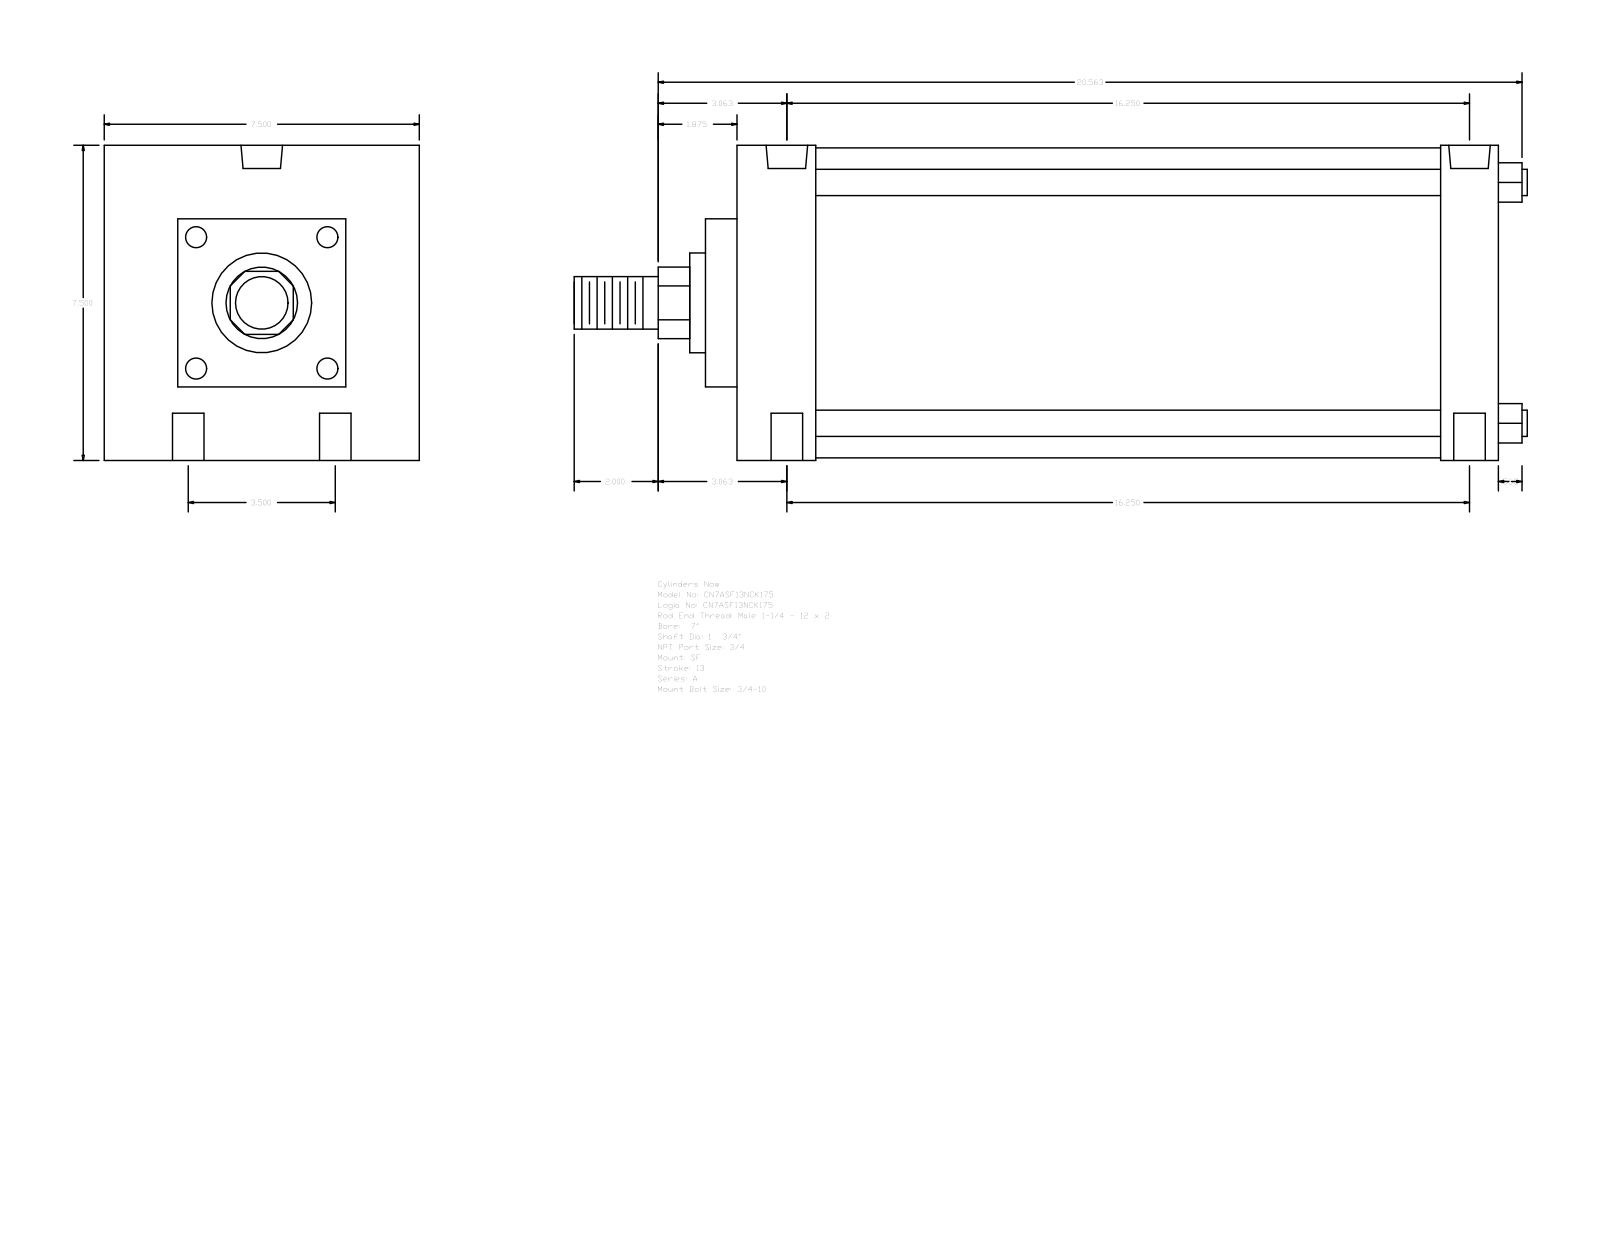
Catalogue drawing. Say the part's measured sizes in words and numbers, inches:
The part is named "A_SF__0700_1.75". Its 3-D file was written by "GSSL Pune (CONFIG_CONTROL_DESIGN)". It is 0 solids with 93 faces: 67 planar, 26 cylindrical and 0 other. Overall it measures 22.687 by 7.5 by 7.5 inches. Round holes: 4 of diameter 0.75, 2 of diameter 0.594, 2 of diameter 0.989. Round bosses or shafts: 4 of diameter 0.625, 1 of diameter 7.375, 1 of diameter 2.375, 1 of diameter 1.75, 1 of diameter 1.25. Partial cylindrical surfaces (rounded edges, fillets, slot ends): 1 of radius 0.852. The main face-to-face distances are 7.5, 18.125, 5.75, 0.75, 1.875, 16.75, 14.875, 16.25, 1.375, 1.75. The hole center spacings are 1.75, 16.344, 16.25, 3.5, 16.623, 15.812.
